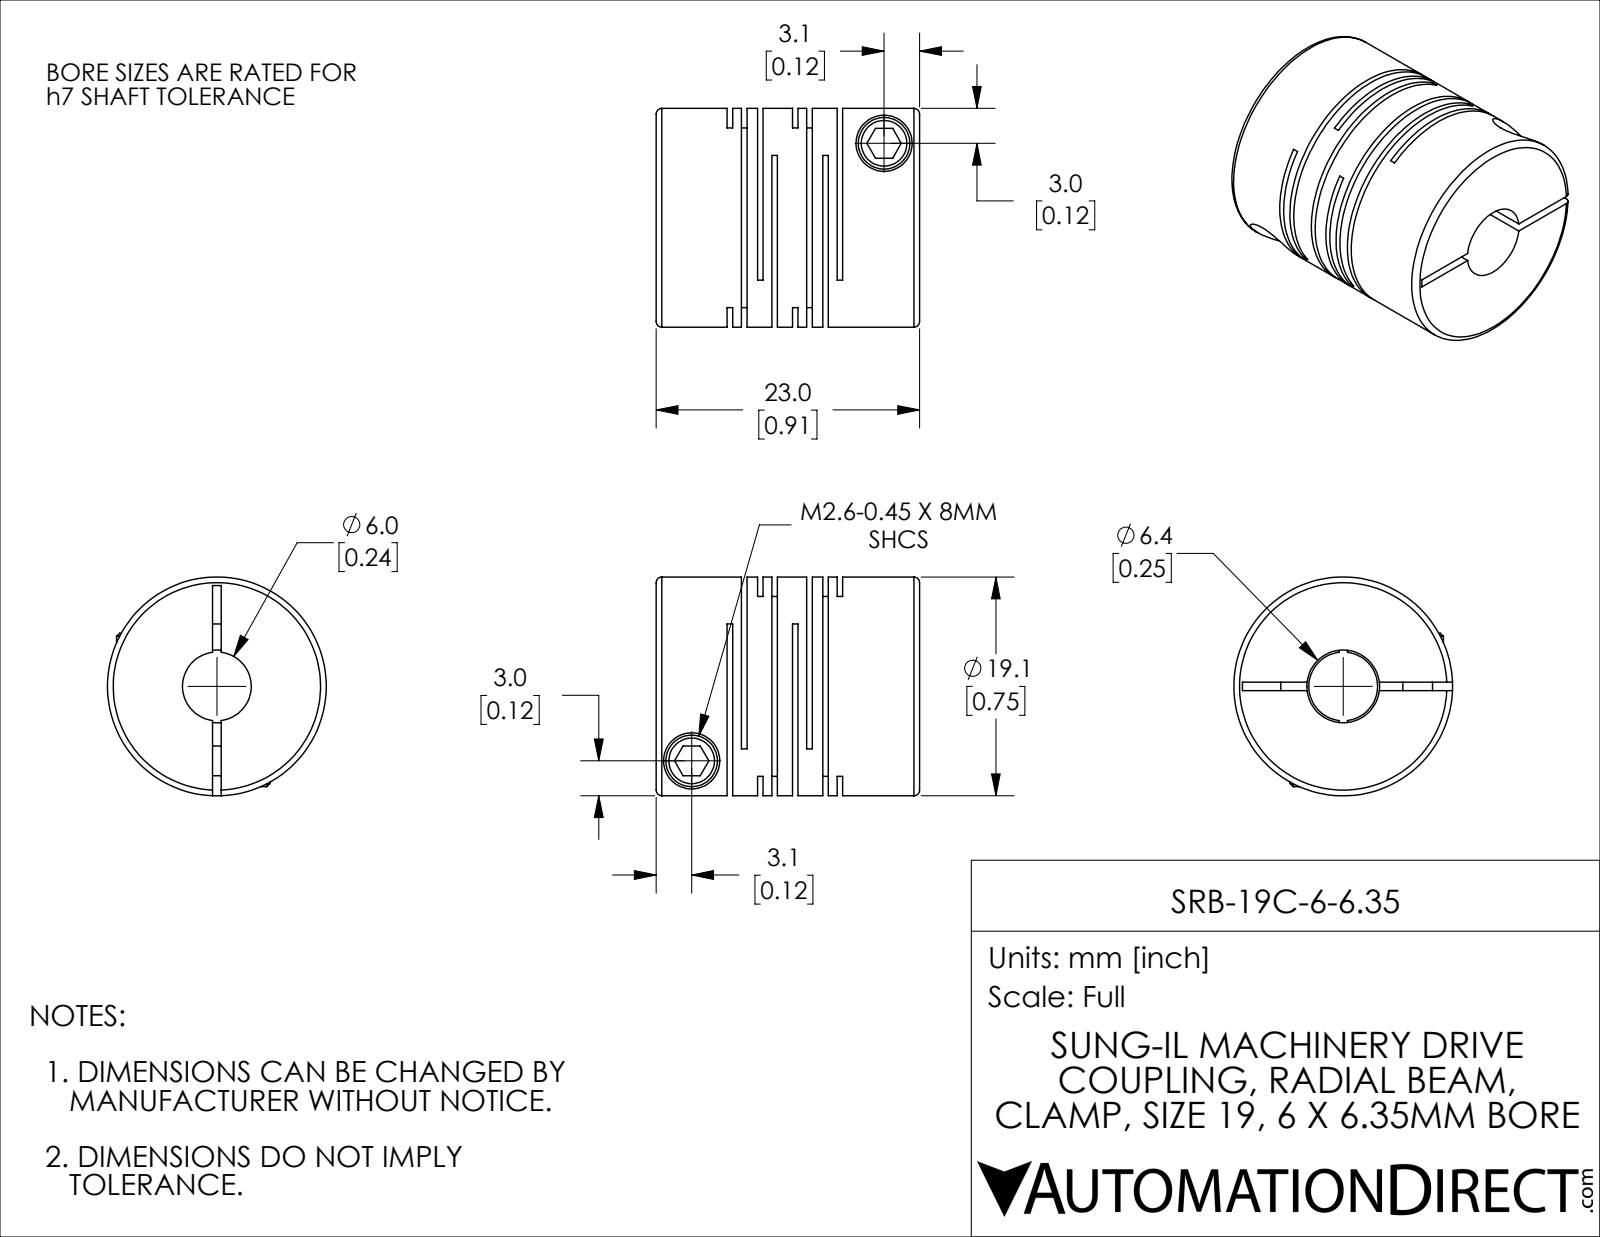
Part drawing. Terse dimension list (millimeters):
name: SRB-19C-6-6
written by: SolidWorks 2021 (CONFIG_CONTROL_DESIGN)
unit: mm
bodies: 1 solid, 114 faces (60 planar, 42 cylindrical, 12 other)
size: 23 × 19.1 × 19.1
volume: 4 881 mm³; area: 6 015 mm²
holes: 2× ⌀2.6, 2× ⌀4.9, 1× ⌀6
bosses: 2× ⌀4.5, 1× ⌀19.1
face distances: 0.48, 1.25, 2.65, 5.7, 2.17, 3.05, 5.22, 4.45, 0.77, 1.4
